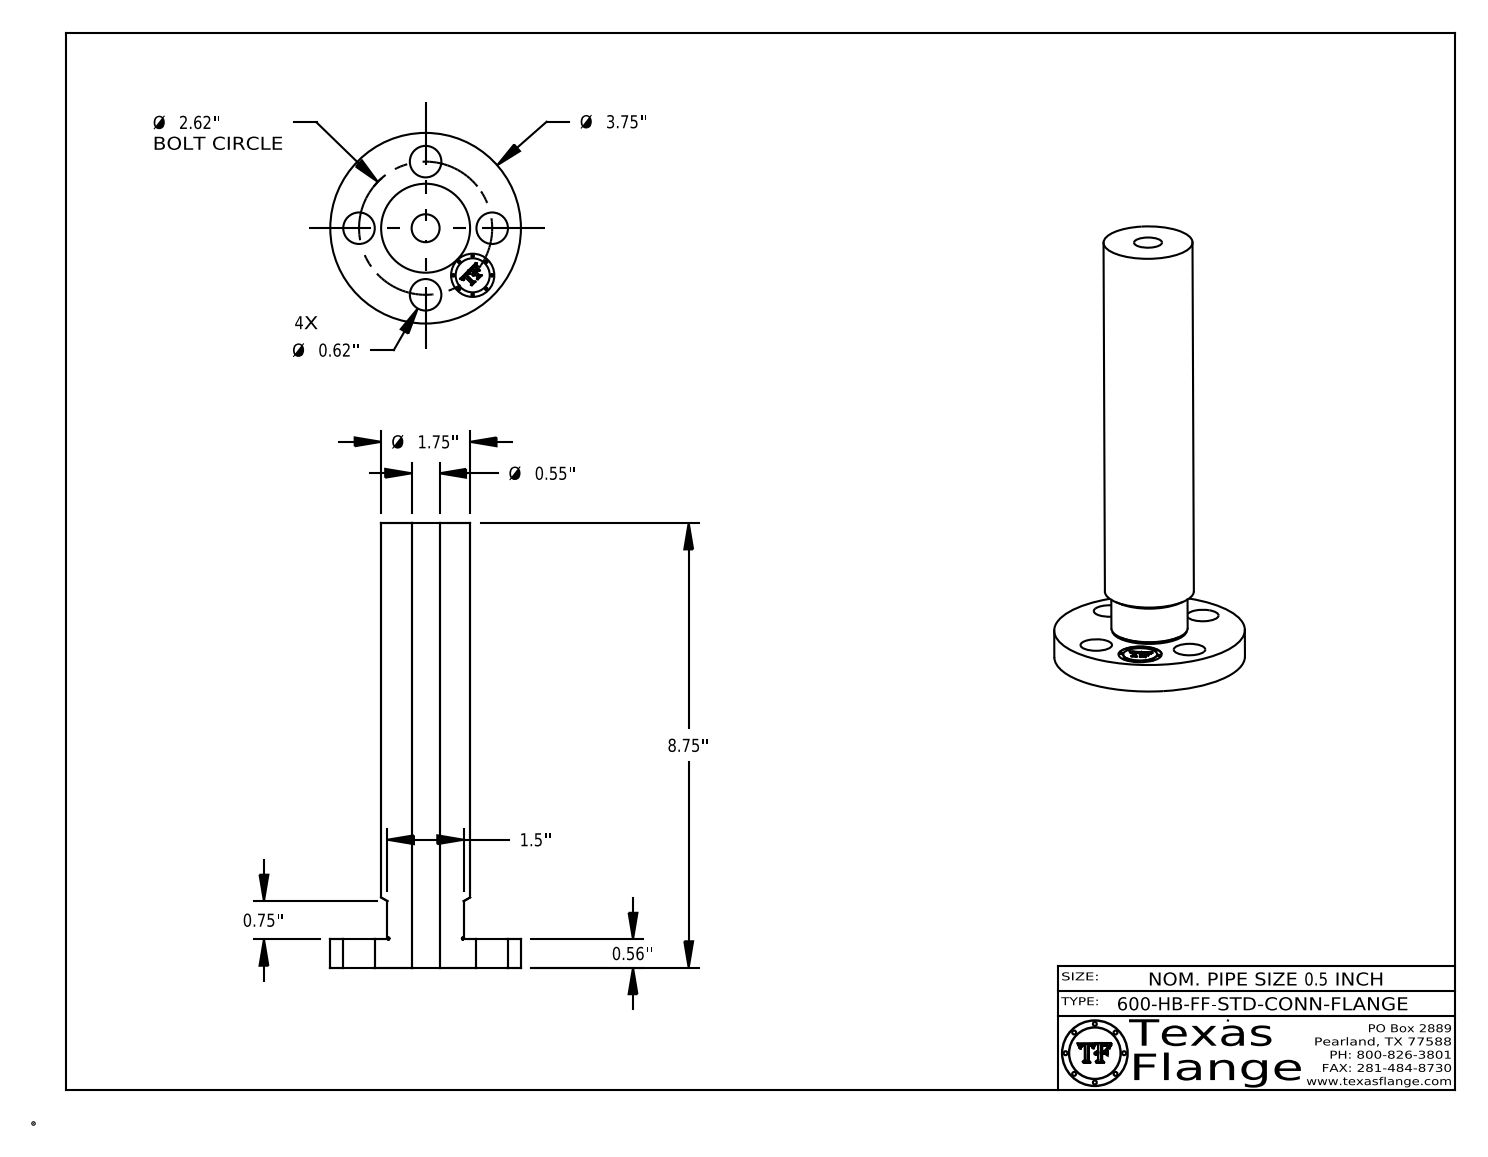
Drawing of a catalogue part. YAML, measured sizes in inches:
part_name: "0.5-600-HB-FF-STD-CONN-FLANGE"
step_written_by: "CATIA V5 STEP AP214 (AUTOMOTIVE_DESIGN)"
units: inches
bodies: {solids: 1, faces: 410, planar: 368, cylindrical: 36, other: 6}
overall_size: [8.75, 3.75, 3.75]
volume: 22.62
surface_area: 90.92
round_holes:
  - {diameter: 0.62, count: 4}
  - {diameter: 0.55, count: 1}
  - {diameter: 0.85, count: 1}
round_bosses_or_shafts:
  - {diameter: 0.051, count: 8}
  - {diameter: 3.75, count: 1}
  - {diameter: 1.75, count: 1}
  - {diameter: 1.5, count: 1}
  - {diameter: 0.67, count: 1}
face_to_face_distances: [0.56, 8.75, 8.19, 0.555, 8.195, 0.254, 0.248, 0.016, 0.046, 0.165]
hole_center_spacings: [1.31, 1.852, 1.003, 2.42, 2.62, 1.31]
